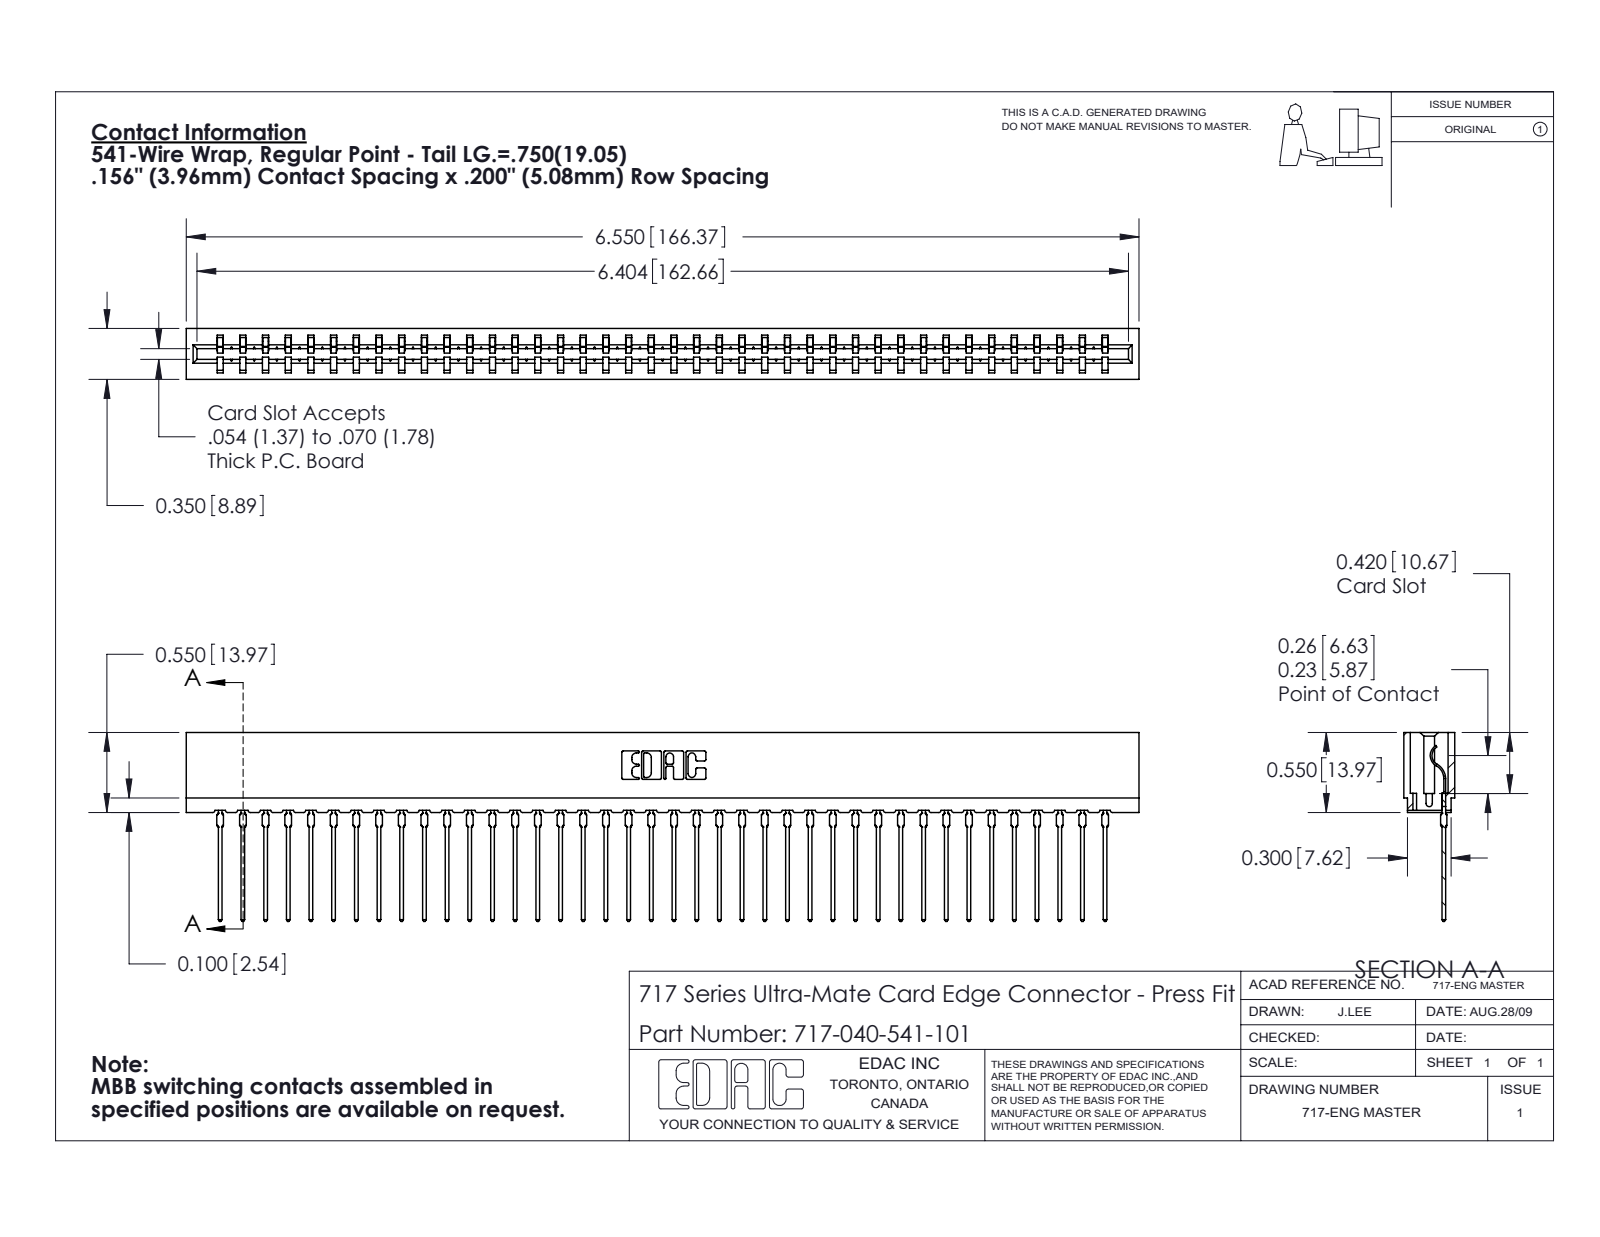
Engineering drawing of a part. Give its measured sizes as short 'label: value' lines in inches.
name: 745-292-001_541; 717 Part_Insulator Option - 06; 717-040-541-101
written by: SolidWorks 2020 (CONFIG_CONTROL_DESIGN)
unit: in
bodies: 41 solids, 4614 faces (2774 planar, 800 cylindrical, 1040 other)
size: 6.55 × 1.299 × 0.35
volume: 0.868 in³; area: 32.25 in²
rounds: 80× R0.015, 80× R0.021, 22× R0.01, 6× R0.007, 6× R0.031, 4× R0.005, 4× R0.011, 3× R0.026
face distances: 0.212, 0.138, 0.35, 0.063, 0.287, 0.076, 0.149, 0.074, 0.045, 0.305
